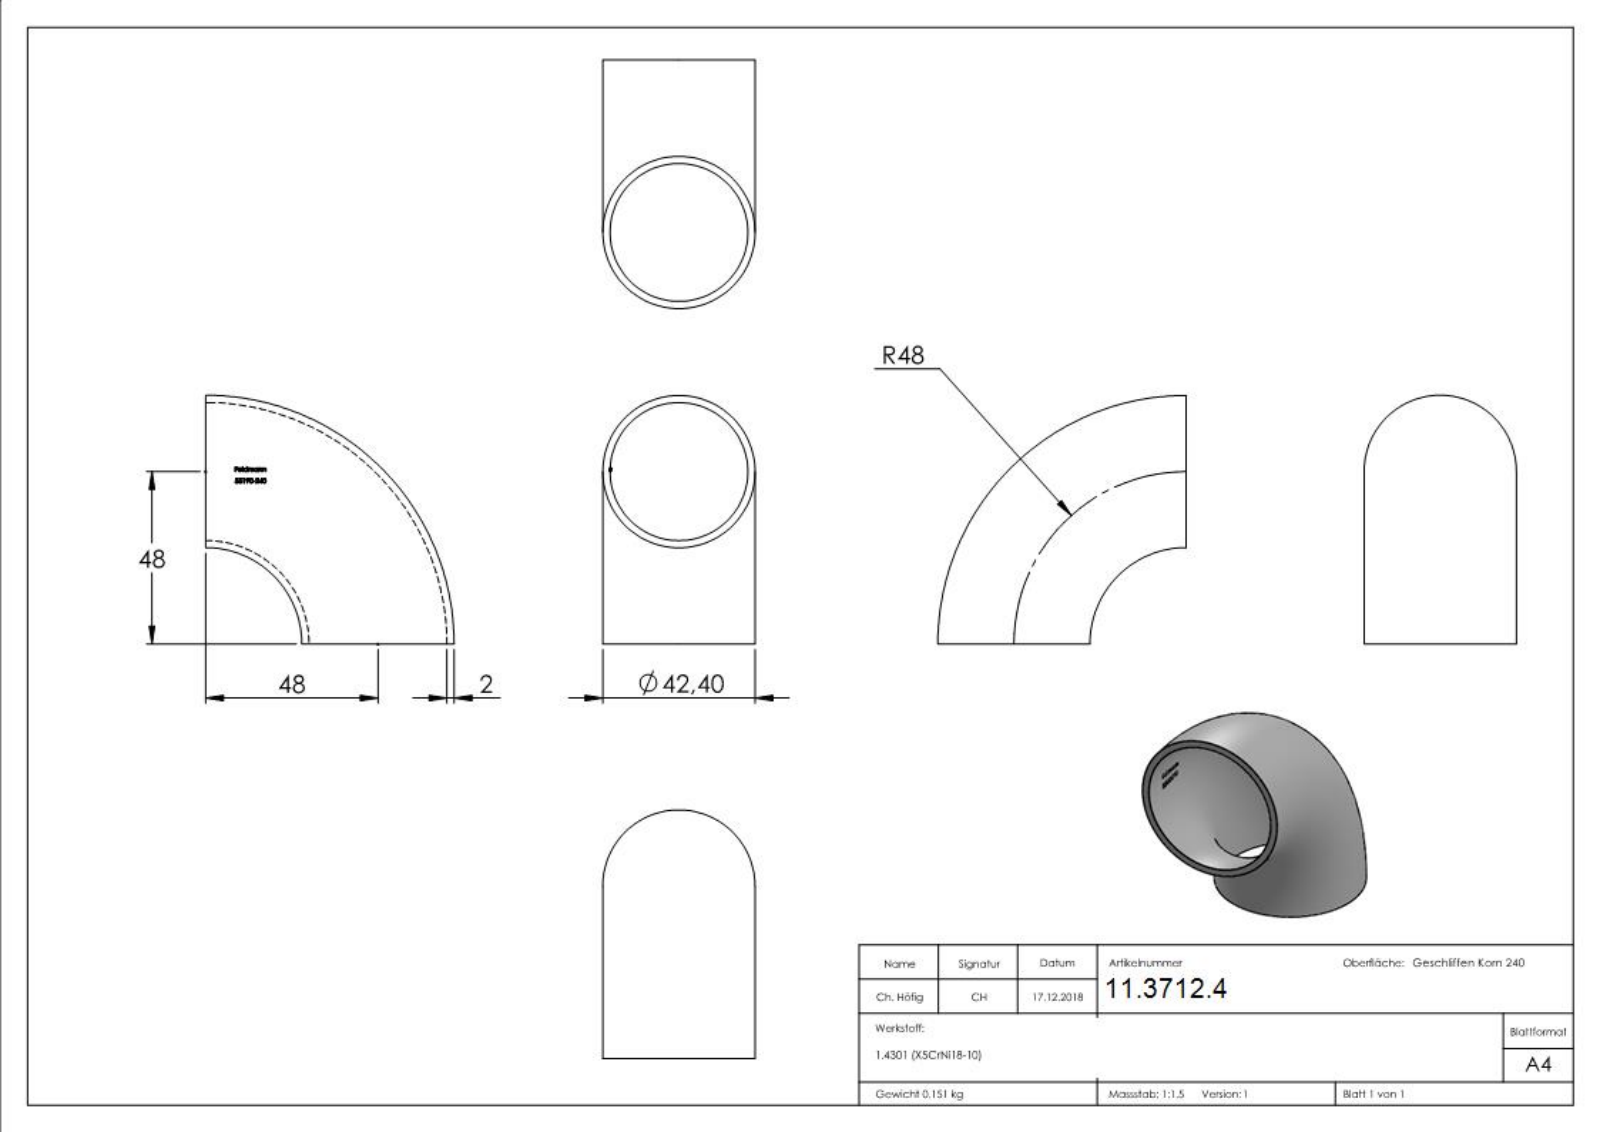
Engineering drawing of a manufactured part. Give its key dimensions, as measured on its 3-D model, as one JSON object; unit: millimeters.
{"part_name": "55190-240", "step_written_by": "SolidWorks 2015 (CONFIG_CONTROL_DESIGN)", "units": "millimeters", "bodies": {"solids": 1, "faces": 225, "planar": 100, "cylindrical": 0, "other": 125}, "overall_size": [69.2, 69.2, 42.4], "volume_mm3": 19139, "surface_area_mm2": 19656, "face_to_face_distances": [0.39, 1.26, 2.97, 1.32, 4.23, 2.02, 3.66, 3.27, 2.4, 0.88]}
